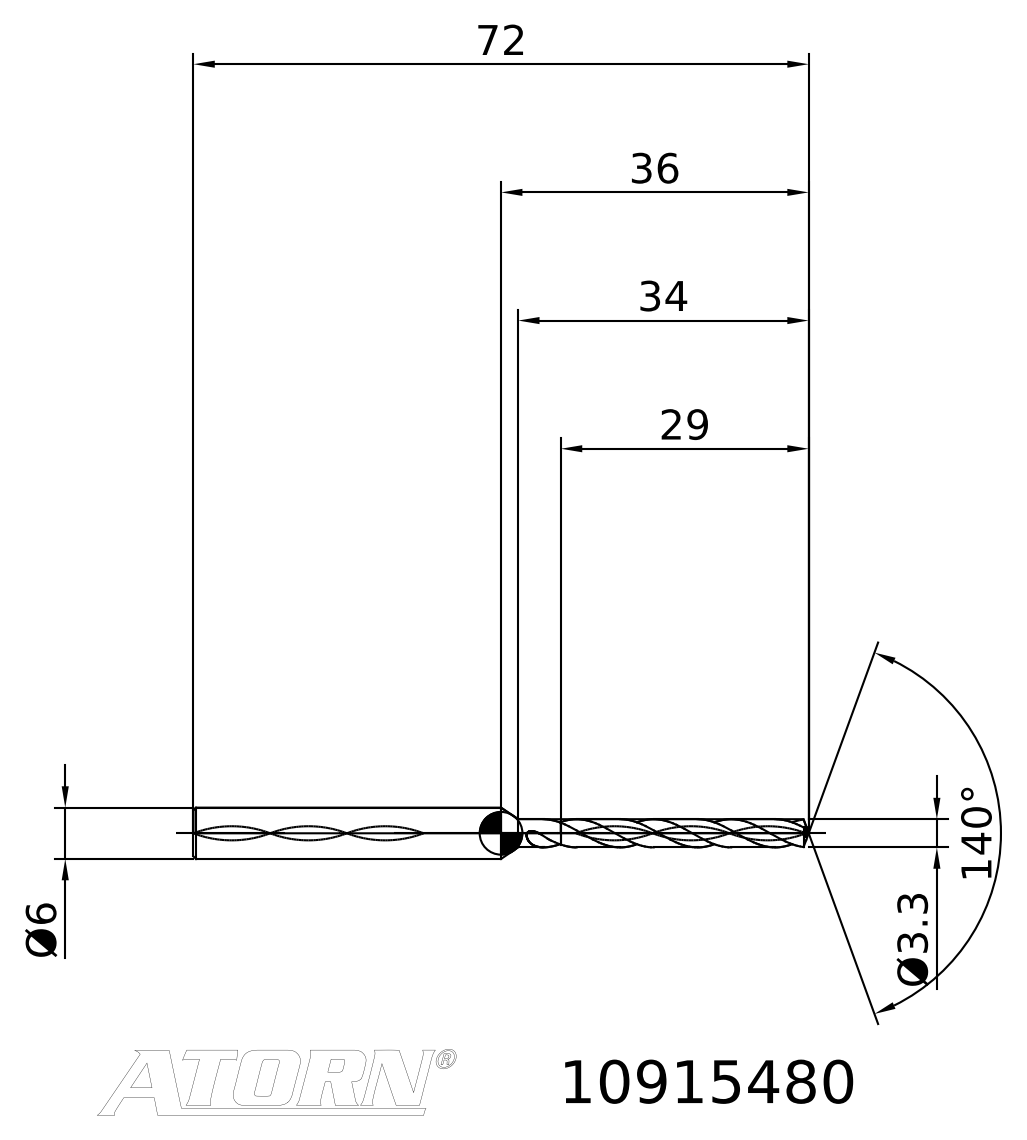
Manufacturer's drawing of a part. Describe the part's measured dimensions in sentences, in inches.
Its 3-D file was written by "TDM (AUTOMOTIVE_DESIGN)". It is 2 solids with 31 faces: 5 planar, 0 cylindrical and 26 other. Overall it measures 2.835 by 0.236 by 0.236 inches. Its volume is 0.076 cubic inches and its surface area 1.761 square inches. The main face-to-face distances are 1.693, 1.124, 2.817.
